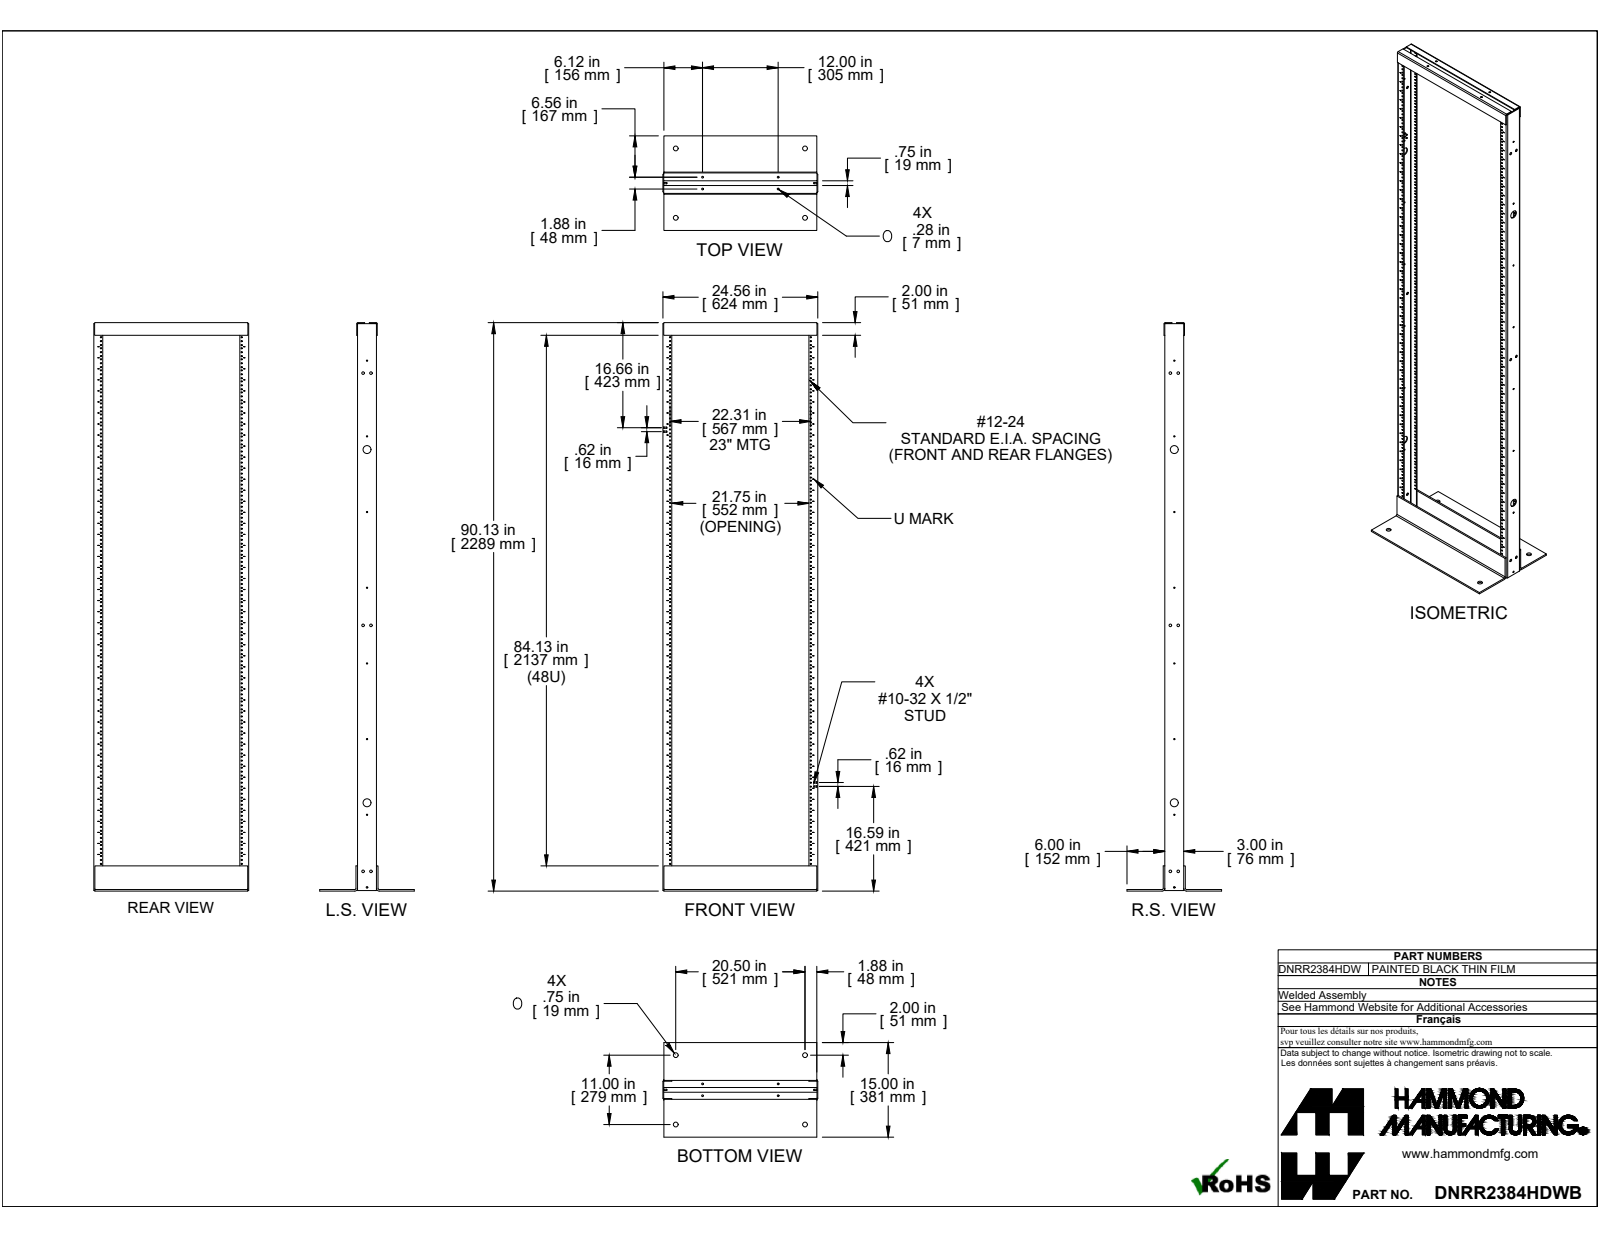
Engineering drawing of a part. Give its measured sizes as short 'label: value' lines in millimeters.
name: DNRR2384HDWB
written by: SolidWorks 2019 (CONFIG_CONTROL_DESIGN)
unit: mm
bodies: 10 solids, 1668 faces (1008 planar, 656 cylindrical, 4 other)
size: 2289.2 × 623.9 × 381
volume: 4 167 000 mm³; area: 2 124 000 mm²
holes: 301× ⌀5.1, 9× ⌀10.3, 4× ⌀7.1, 4× ⌀19.1, 2× ⌀31.8, 1× ⌀6.4
bosses: 4× ⌀6.4, 4× ⌀4.8
rounds: 6× R1.5, 6× R4.7, 2× R2.8, 2× R4.8, 2× R11.1
face distances: 3.2, 3.2, 6.4, 76.2, 79.4, 617.5, 620.7, 623.9, 620.7, 73
hole spacings: 44.5, 88.9, 133.4, 177.8, 222.3, 31.8, 266.7, 15.9
